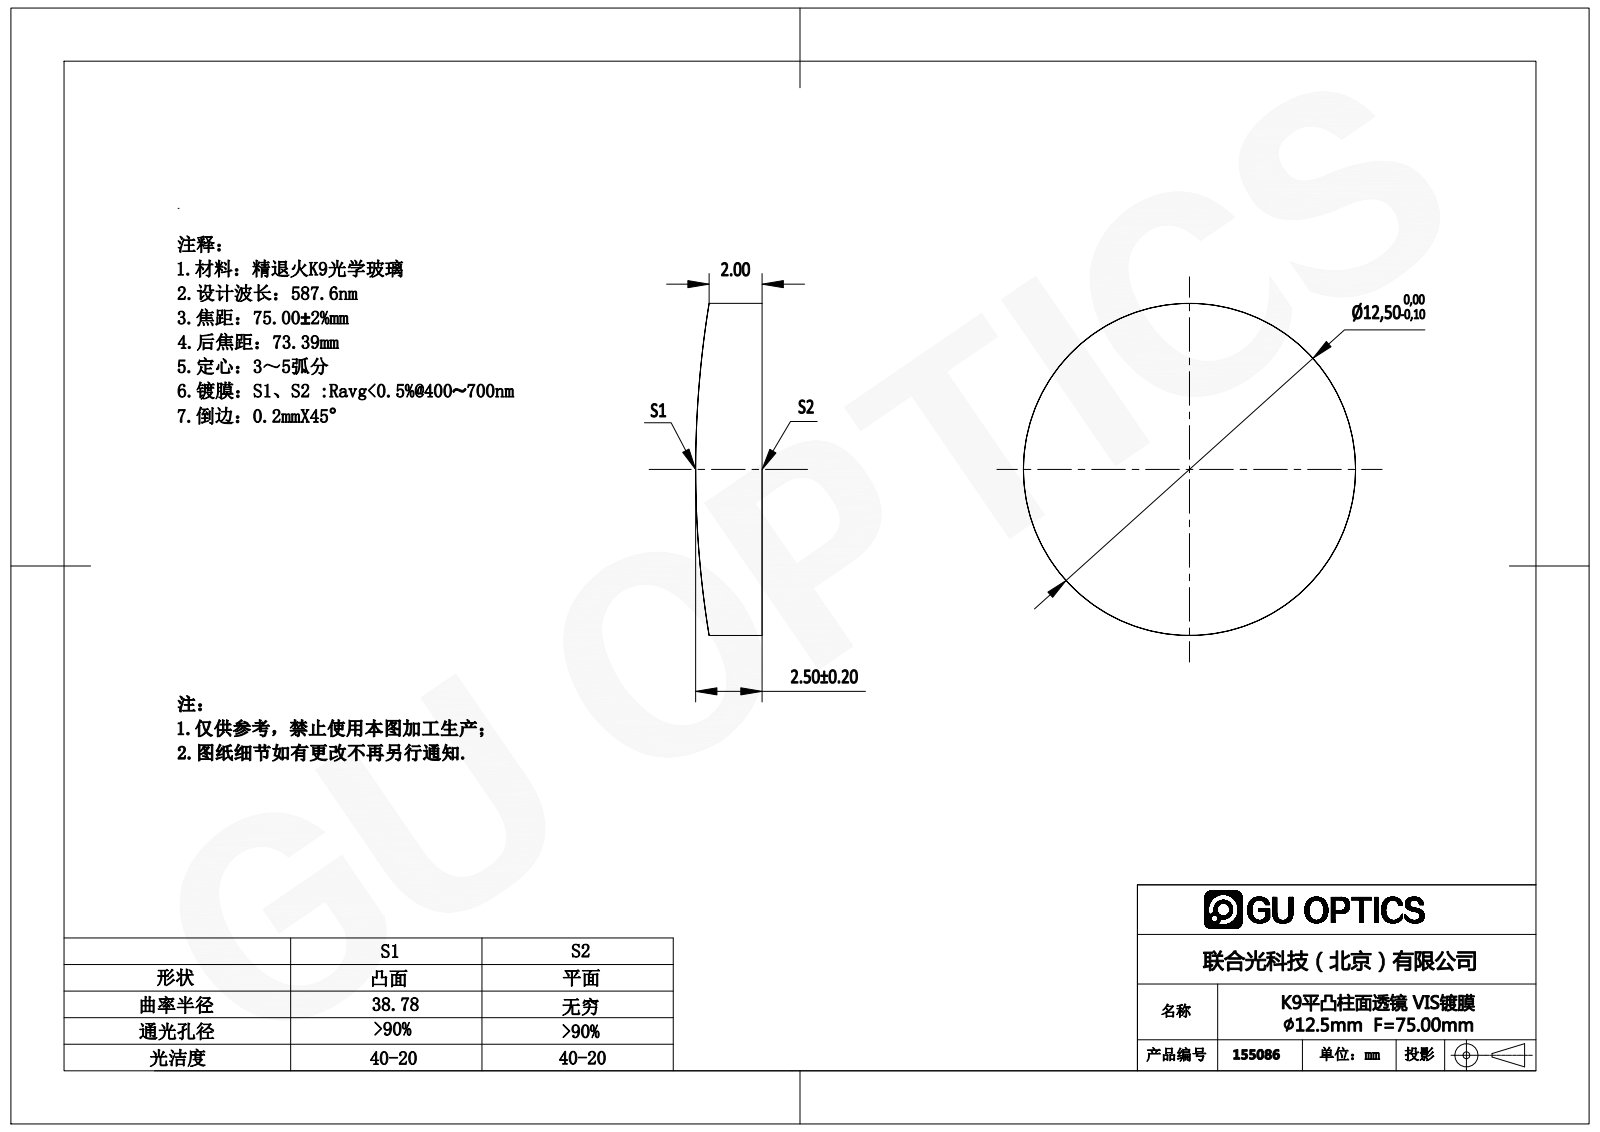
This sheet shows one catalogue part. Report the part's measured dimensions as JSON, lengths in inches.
{"part_name": "155020", "step_written_by": "SolidWorks 2016 (AUTOMOTIVE_DESIGN)", "units": "inches", "bodies": {"solids": 1, "faces": 4, "planar": 1, "cylindrical": 3, "other": 0}, "overall_size": [0.492, 0.492, 0.098], "volume_in3": 0.018, "surface_area_in2": 0.518, "round_bosses_or_shafts": [[0.492, 1]], "partial_cylinders_radius": [[1.527, 1]]}
